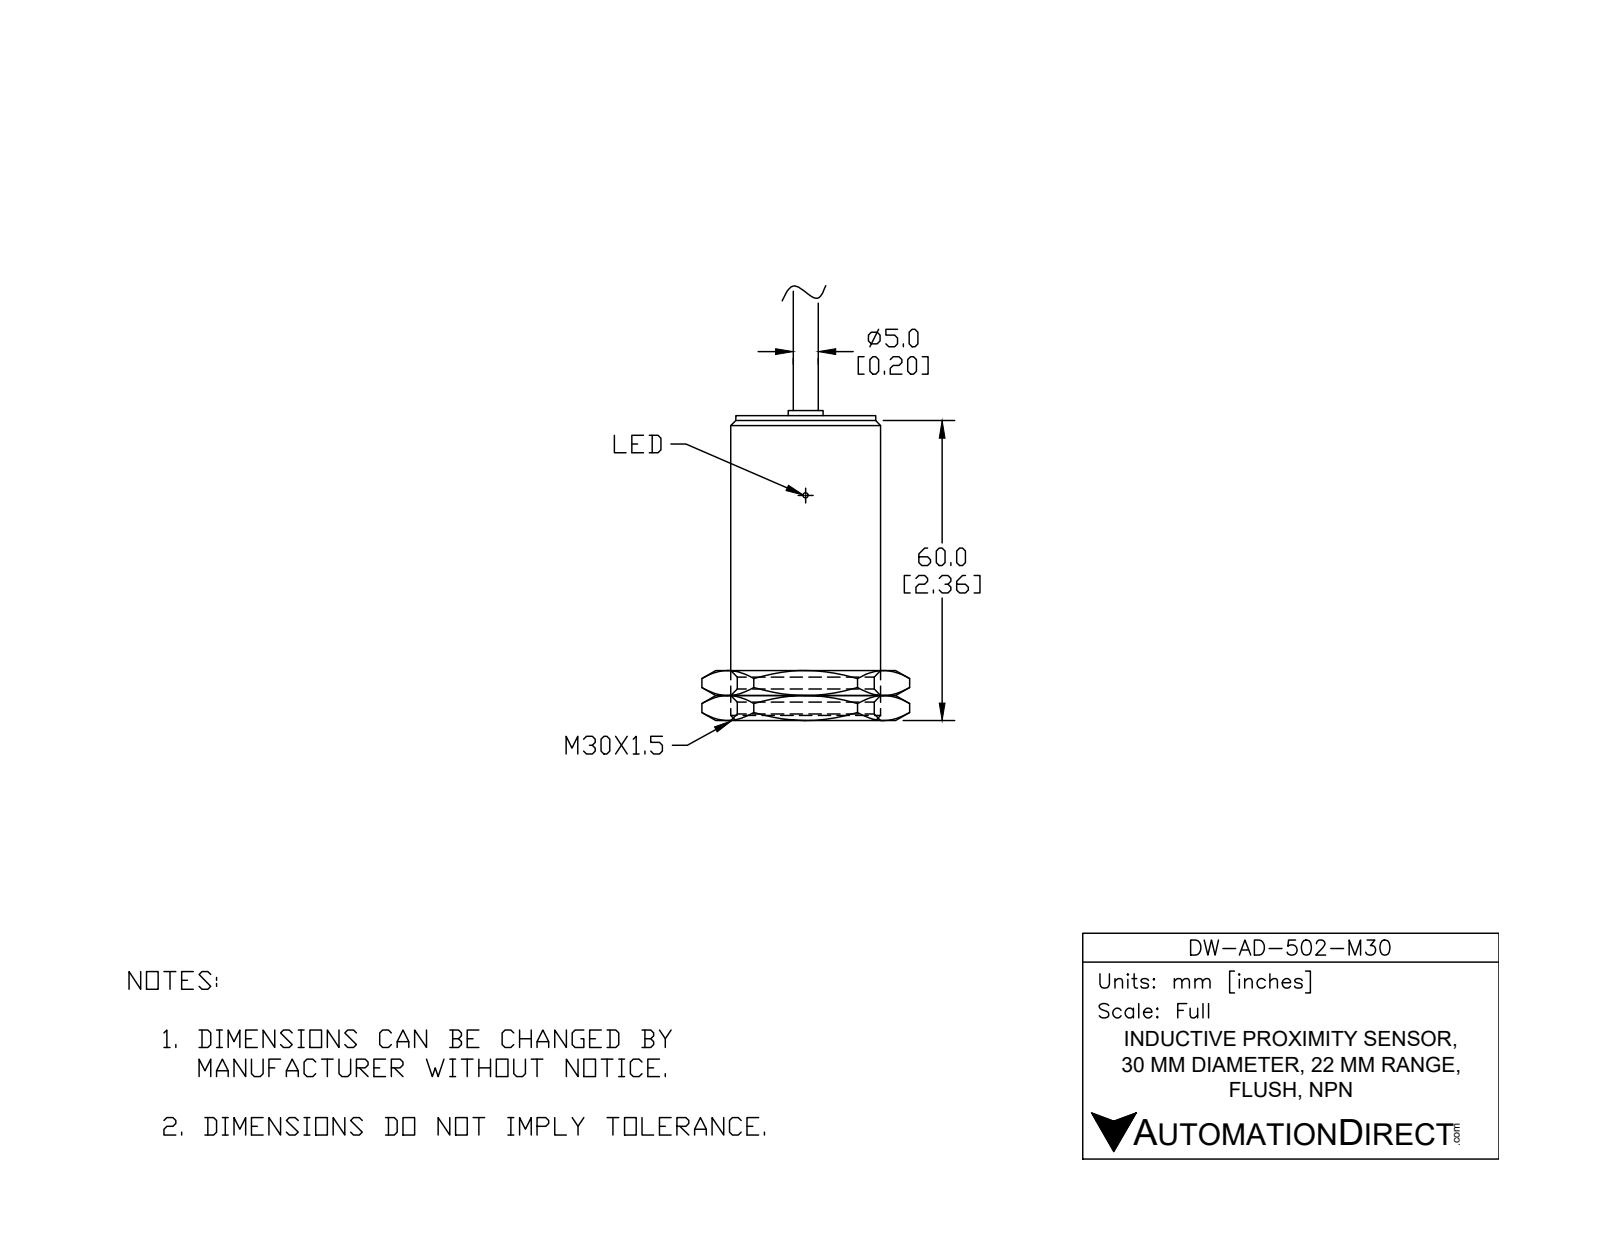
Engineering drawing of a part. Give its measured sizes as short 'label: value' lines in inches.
name: DW-AD-502-M30
written by: SolidWorks 2017 (AUTOMOTIVE_DESIGN)
unit: in
bodies: 2 solids, 31 faces (17 planar, 5 cylindrical, 9 other)
size: 3.409 × 1.181 × 1.181
volume: 2.658 in³; area: 11.68 in²
bosses: 1× ⌀1.181, 1× ⌀1.083, 1× ⌀0.413, 1× ⌀0.268, 1× ⌀0.197
face distances: 2.402, 2.48, 0.079, 0.031, 2.433, 0.047, 2.283, 0.118, 0.15, 0.197
